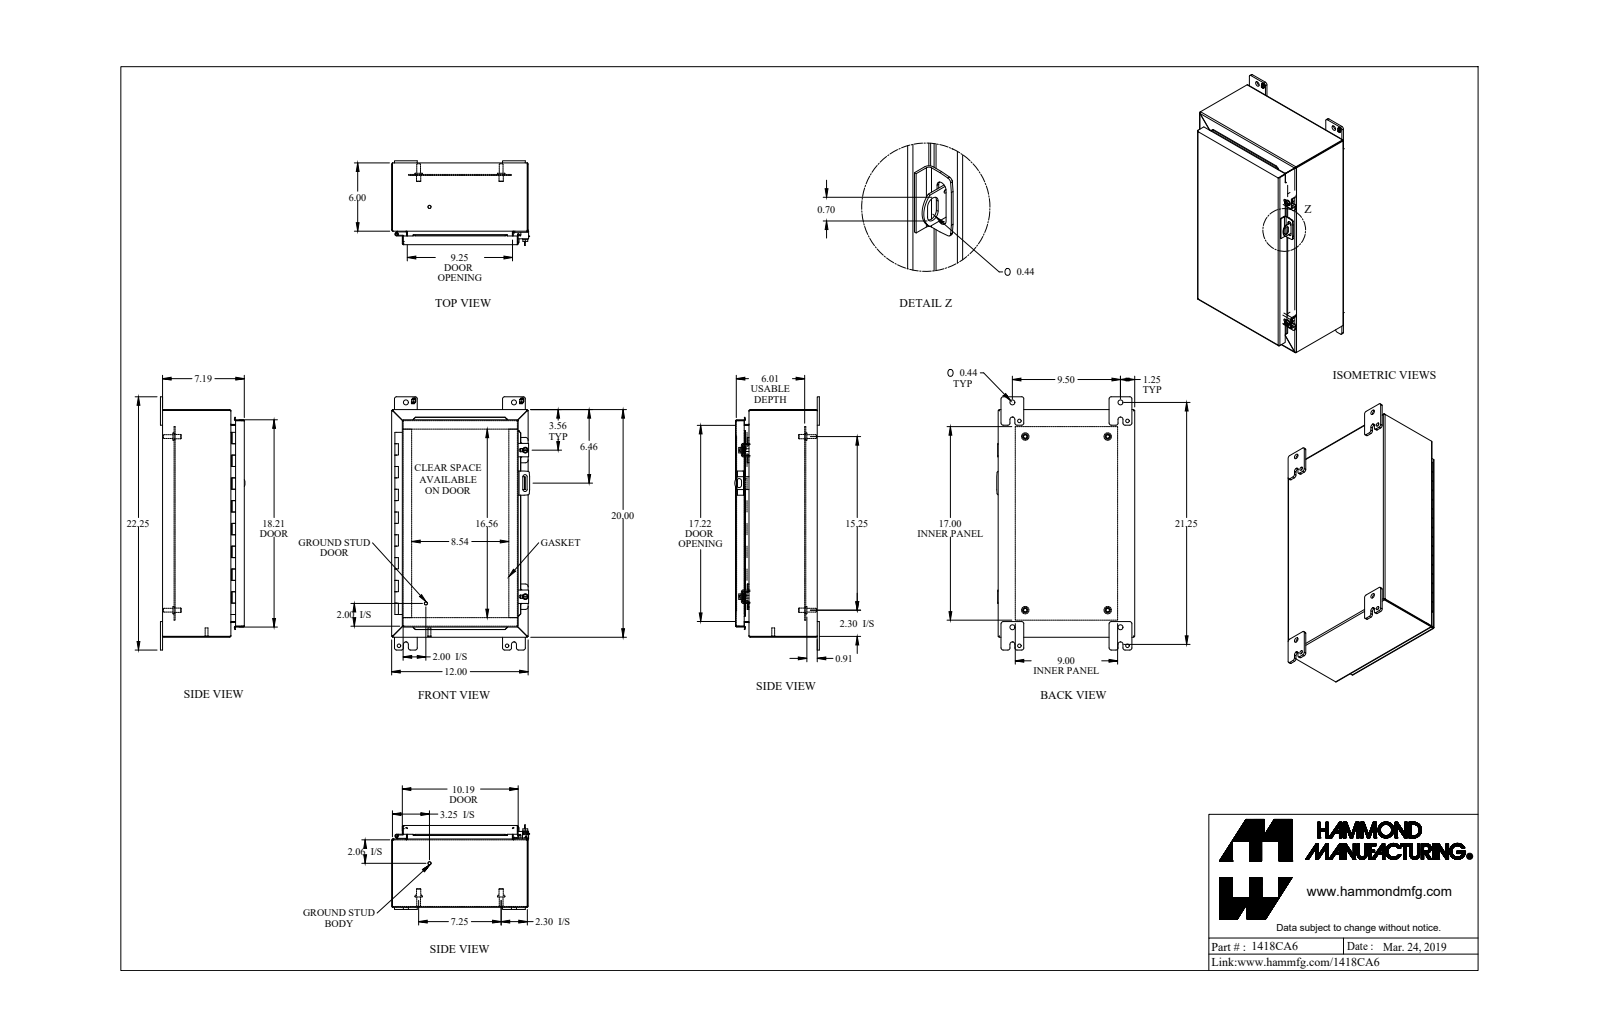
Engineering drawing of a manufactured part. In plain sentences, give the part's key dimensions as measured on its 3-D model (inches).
The part is named "1418CA6". Its 3-D file was written by "SolidWorks 2019 (AUTOMOTIVE_DESIGN)". It is 38 solids with 970 faces: 667 planar, 251 cylindrical and 52 other. Overall it measures 22.25 by 12.125 by 7.437 inches. Its volume is 101.5 cubic inches and its surface area 2 633 square inches. Round holes: 4 of diameter 0.313, 4 of diameter 0.437, 4 of diameter 0.5, 2 of diameter 0.213, 2 of diameter 0.265, 2 of diameter 0.307, 2 of diameter 0.375, 2 of diameter 0.445, 1 of diameter 0.125, 1 of diameter 0.187. Round bosses or shafts: 4 of diameter 0.65, 4 of diameter 0.375, 4 of diameter 0.33, 2 of diameter 1, 2 of diameter 0.5, 2 of diameter 0.39, 2 of diameter 0.281, 2 of diameter 0.25. Partial cylindrical surfaces (rounded edges, fillets, slot ends): 26 of radius 0.188, 20 of radius 0.036, 20 of radius 0.108, 13 of radius 0.048, 13 of radius 0.143, 8 of radius 0.007, 8 of radius 0.045, 8 of radius 0.079. The main face-to-face distances are 0.072, 7.113, 7.041, 11.928, 0.937, 7.185, 1.009, 0.095, 6.081, 6.009. The hole center spacings are 9.5, 1.736, 8.508, 16.886, 19.75, 21.916, 1.875, 2.434.
